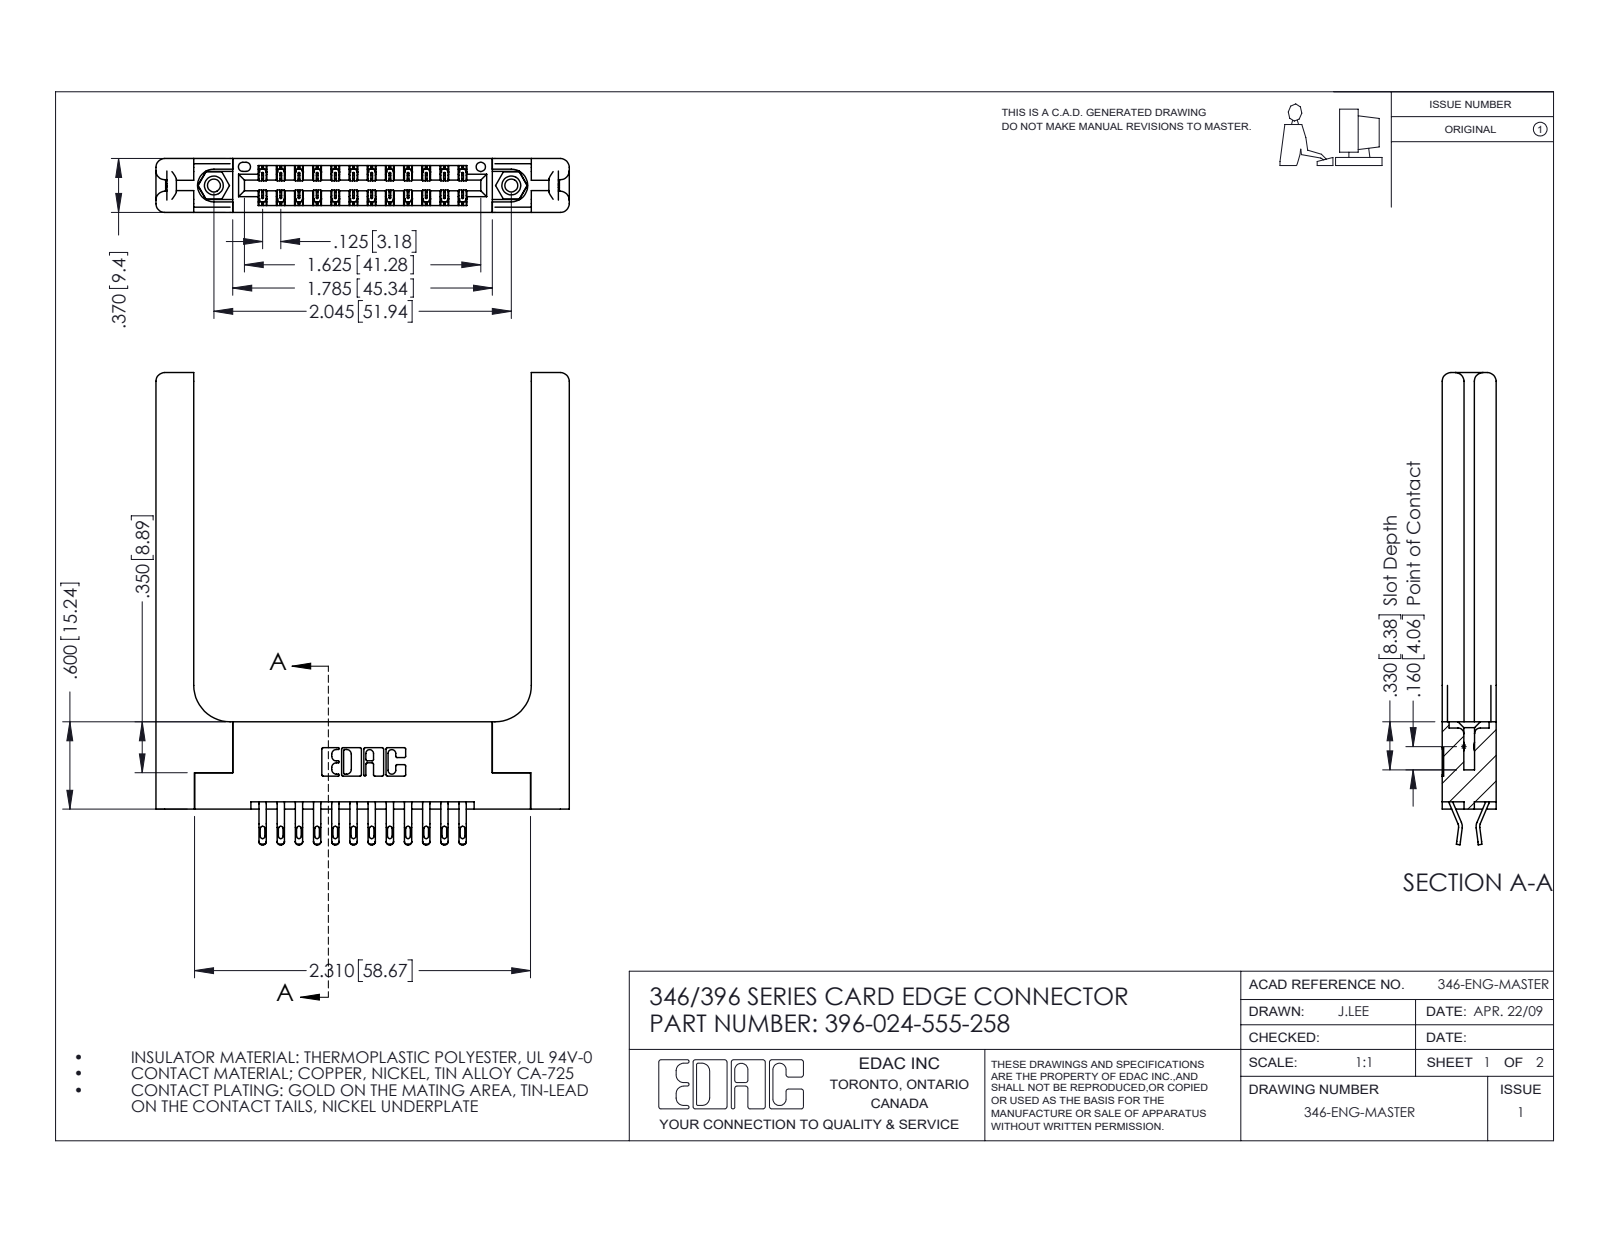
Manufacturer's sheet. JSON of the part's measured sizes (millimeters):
{"part_name": "346 Part_Flush Mounting Lugs - 0.156 Dia-TH; 345-292-001_555 Tail; 345-250-001_345-250-001-102; 346-220-058_345-220-058 (+1 more)", "step_written_by": "SolidWorks 2016 (CONFIG_CONTROL_DESIGN)", "units": "millimeters", "bodies": {"solids": 29, "faces": 1770, "planar": 1016, "cylindrical": 694, "other": 60}, "overall_size": [82.4, 72.2, 9.4], "volume_mm3": 14400, "surface_area_mm2": 14200, "round_holes": [[2.3, 2], [3.2, 2], [4, 2], [1.6, 1]], "round_bosses_or_shafts": [[3.9, 2]], "partial_cylinders_radius": [[0.4, 48], [0.5, 48], [0.2, 36], [0.3, 22], [1.5, 16], [0.2, 6], [0.8, 6], [0.7, 3]], "face_to_face_distances": [9.4, 3.8, 1.8, 3.8, 1.2, 8.2, 2.6, 5.6, 4.4, 6.4], "hole_center_spacings": [6.2, 46.7, 51.9]}
